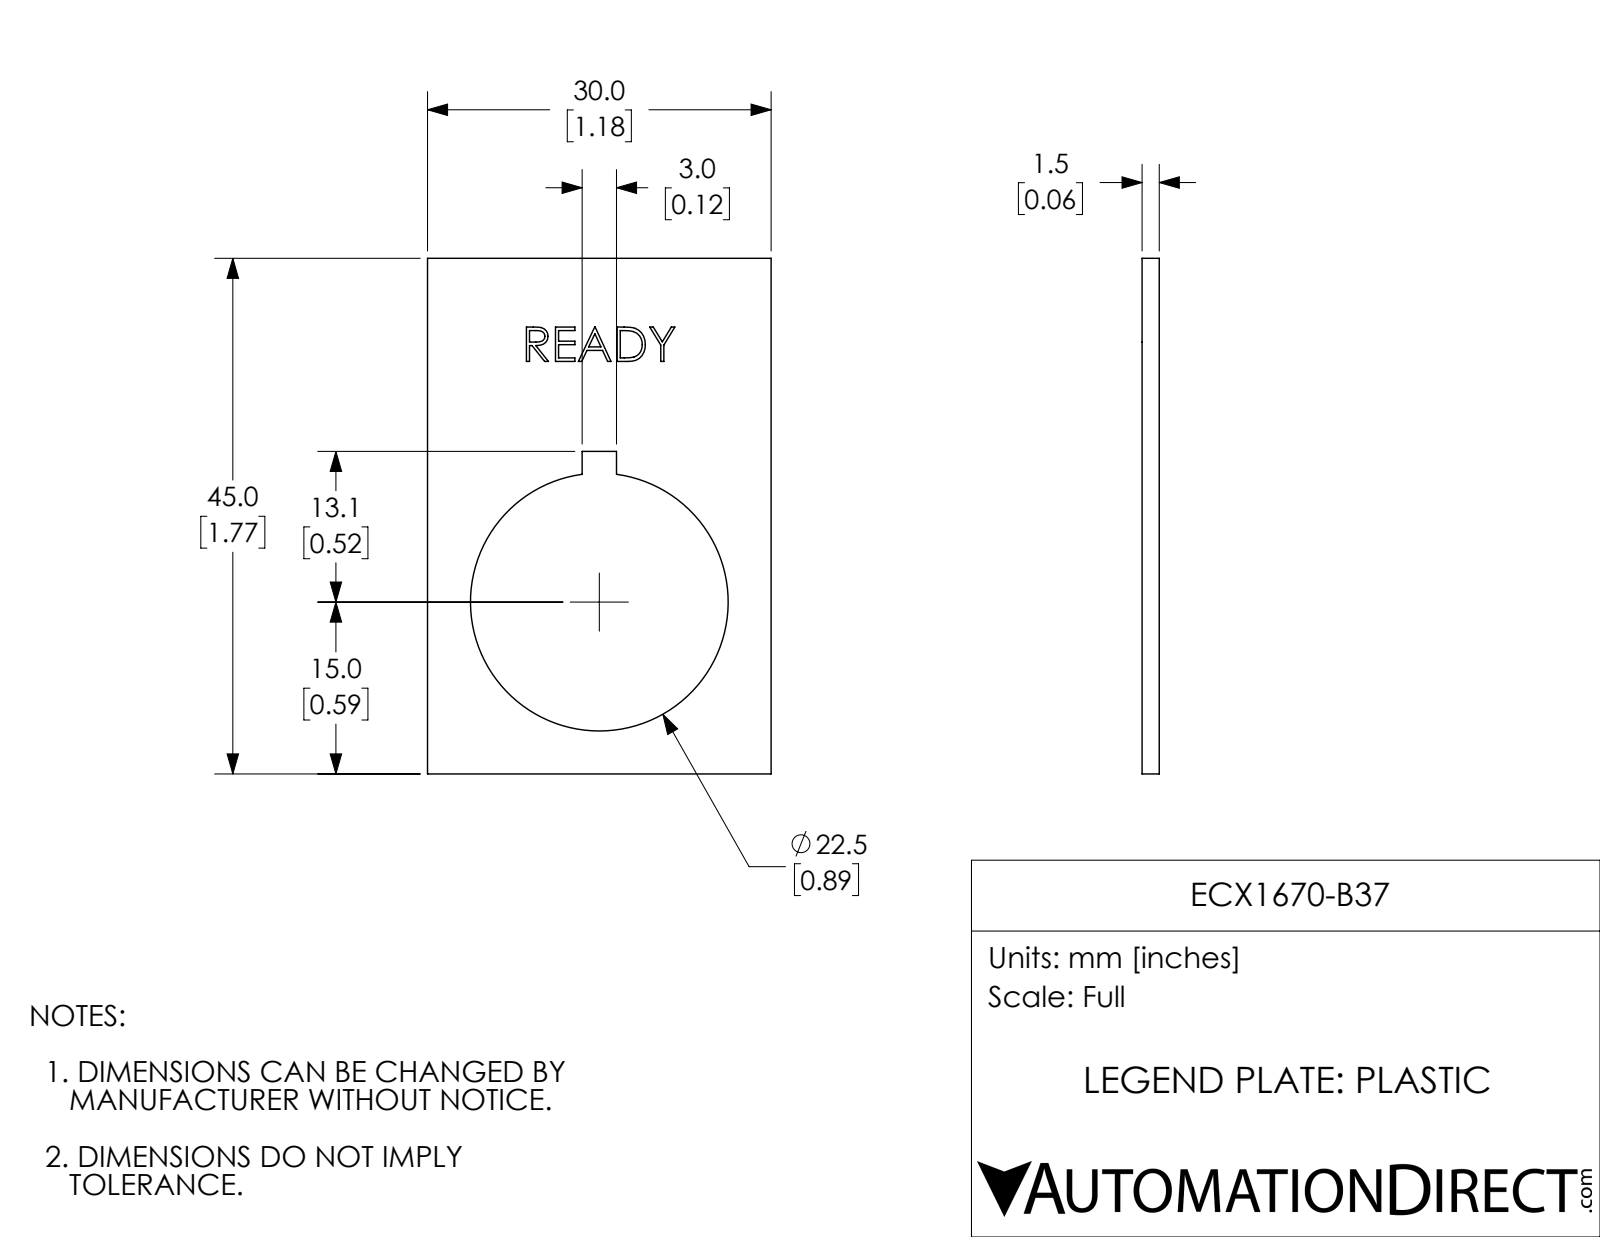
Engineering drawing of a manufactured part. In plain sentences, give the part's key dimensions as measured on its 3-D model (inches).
The part is named "ECX1670-B37". Its 3-D file was written by "SolidWorks 2017 (AUTOMOTIVE_DESIGN)". It is 1 solid with 81 faces: 66 planar, 3 cylindrical and 12 other. Overall it measures 1.772 by 1.181 by 0.059 inches. Its volume is 0.087 cubic inches and its surface area 3.46 square inches. Round holes: 1 of diameter 0.886. The main face-to-face distances are 0.059, 1.181, 1.772, 0.058, 0.531, 0.65, 1.108, 0.663, 0.118, 0.012.
